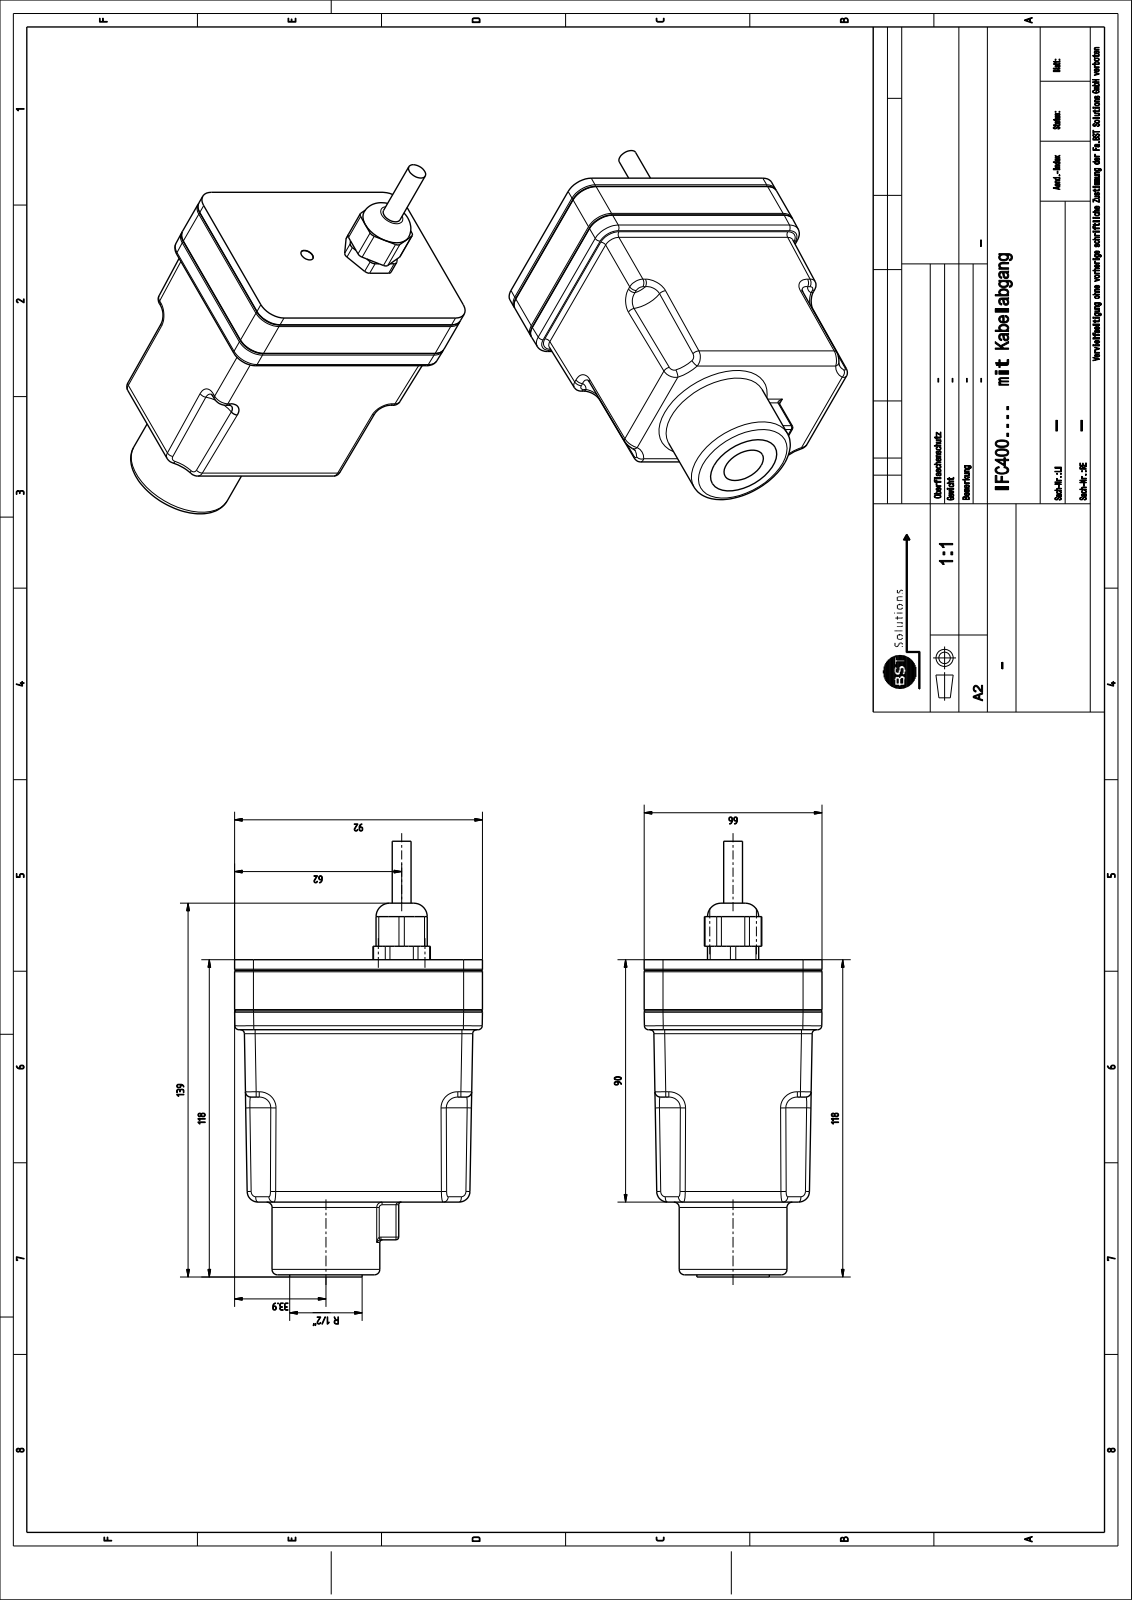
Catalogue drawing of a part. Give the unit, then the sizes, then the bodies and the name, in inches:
Units: inches
Overall size (bounding box): 6.37 × 3.622 × 2.598
Round holes (diameter × count): ⌀0.63 ×2, ⌀0.13 ×1, ⌀0.197 ×1, ⌀0.906 ×1, ⌀0.945 ×1
Round bosses / shafts (diameter × count): ⌀1.575 ×1, ⌀1.059 ×1, ⌀0.276 ×1
Partial cylindrical surfaces — rounded edges, fillets, slot ends (radius × count): R0.02 ×16, R0.079 ×16, R0.039 ×10, R0.059 ×8, R0.157 ×8, R0.276 ×8, R0.394 ×4
Main face-to-face distances: 0.591, 0.748, 0.157, 2.795, 3.386, 3.543, 2.598, 0.137, 3.622, 1.063
Hole centre spacings: 1.102, 1.106
Volume: 30.35 in³ · Surface area: 109.1 in²
Bodies: 4 solids, 236 faces (70 planar, 89 cylindrical, 77 other)
Part name (STEP PRODUCT): 1616411020; 1615286318; 1615281506; 1615456404
STEP written by: Spatial InterOp 3D (AUTOMOTIVE_DESIGN)
